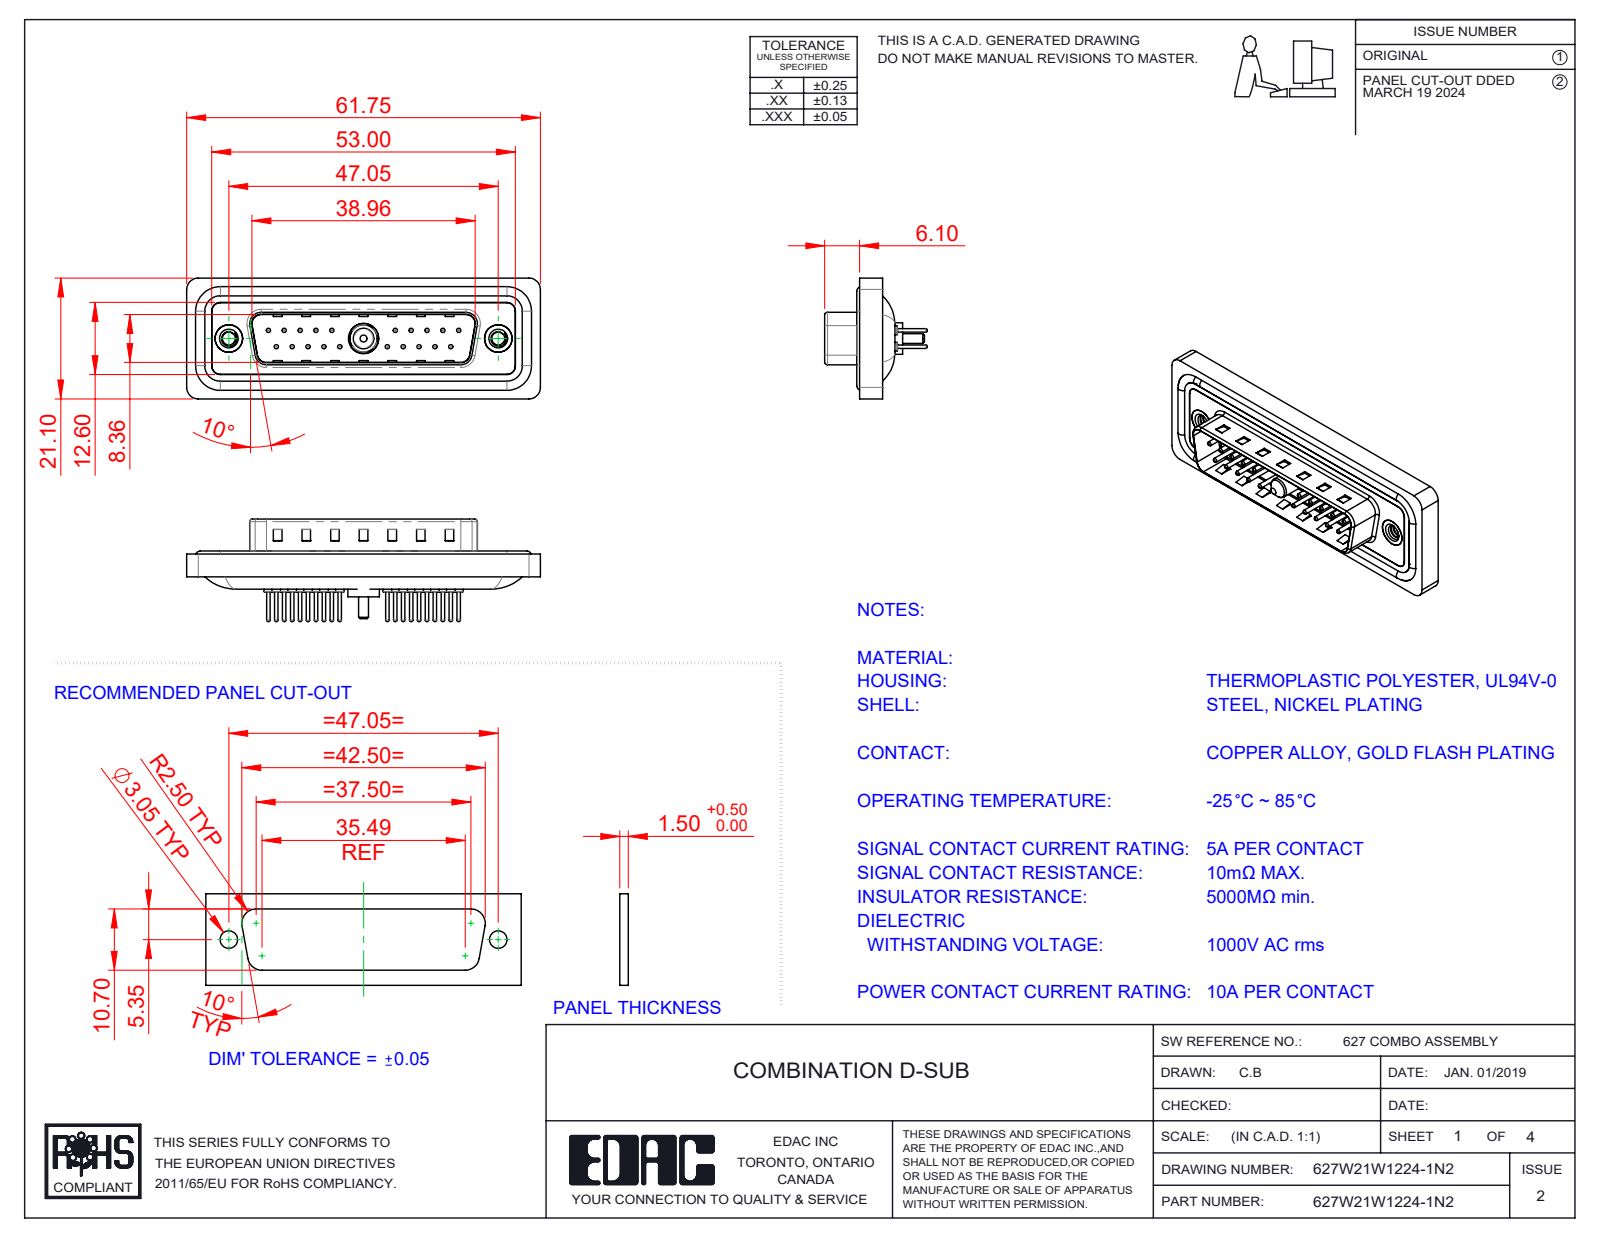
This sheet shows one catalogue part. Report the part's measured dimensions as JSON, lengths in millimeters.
{"part_name": "627Combo Waterproof Housing_25 Contacts; Power Pin_10A S; 627Combo Contact Row 1_24; 627Combo Contact Row 2_24 (+5 more)", "step_written_by": "SolidWorks 2023 (CONFIG_CONTROL_DESIGN)", "units": "millimeters", "bodies": {"solids": 29, "faces": 1262, "planar": 359, "cylindrical": 487, "other": 416}, "overall_size": [61.75, 21.1, 17.9], "volume_mm3": 7183, "surface_area_mm2": 11941, "round_holes": [[0.75, 20], [1.6, 20], [2, 20], [2.26, 2], [4, 2], [4.8, 2], [5, 2], [4.85, 1], [5.3, 1]], "round_bosses_or_shafts": [[1.5, 20], [0.6, 20], [1.6, 4], [4.9, 2], [5.5, 1], [5.2, 1], [4.75, 1], [3.75, 1]], "partial_cylinders_radius": [[1.5, 22], [2, 18], [0.5, 8], [1.6, 8], [0.25, 4], [0.6, 4], [0.65, 4], [0.9, 4]], "face_to_face_distances": [0.4, 1.5, 1.1, 1.6, 0.5, 3.1, 2.9, 4.1, 0.82, 9.58], "hole_center_spacings": [3.16, 2.77, 5.54, 8.31, 5.04, 19.39, 20.97, 22.16]}
